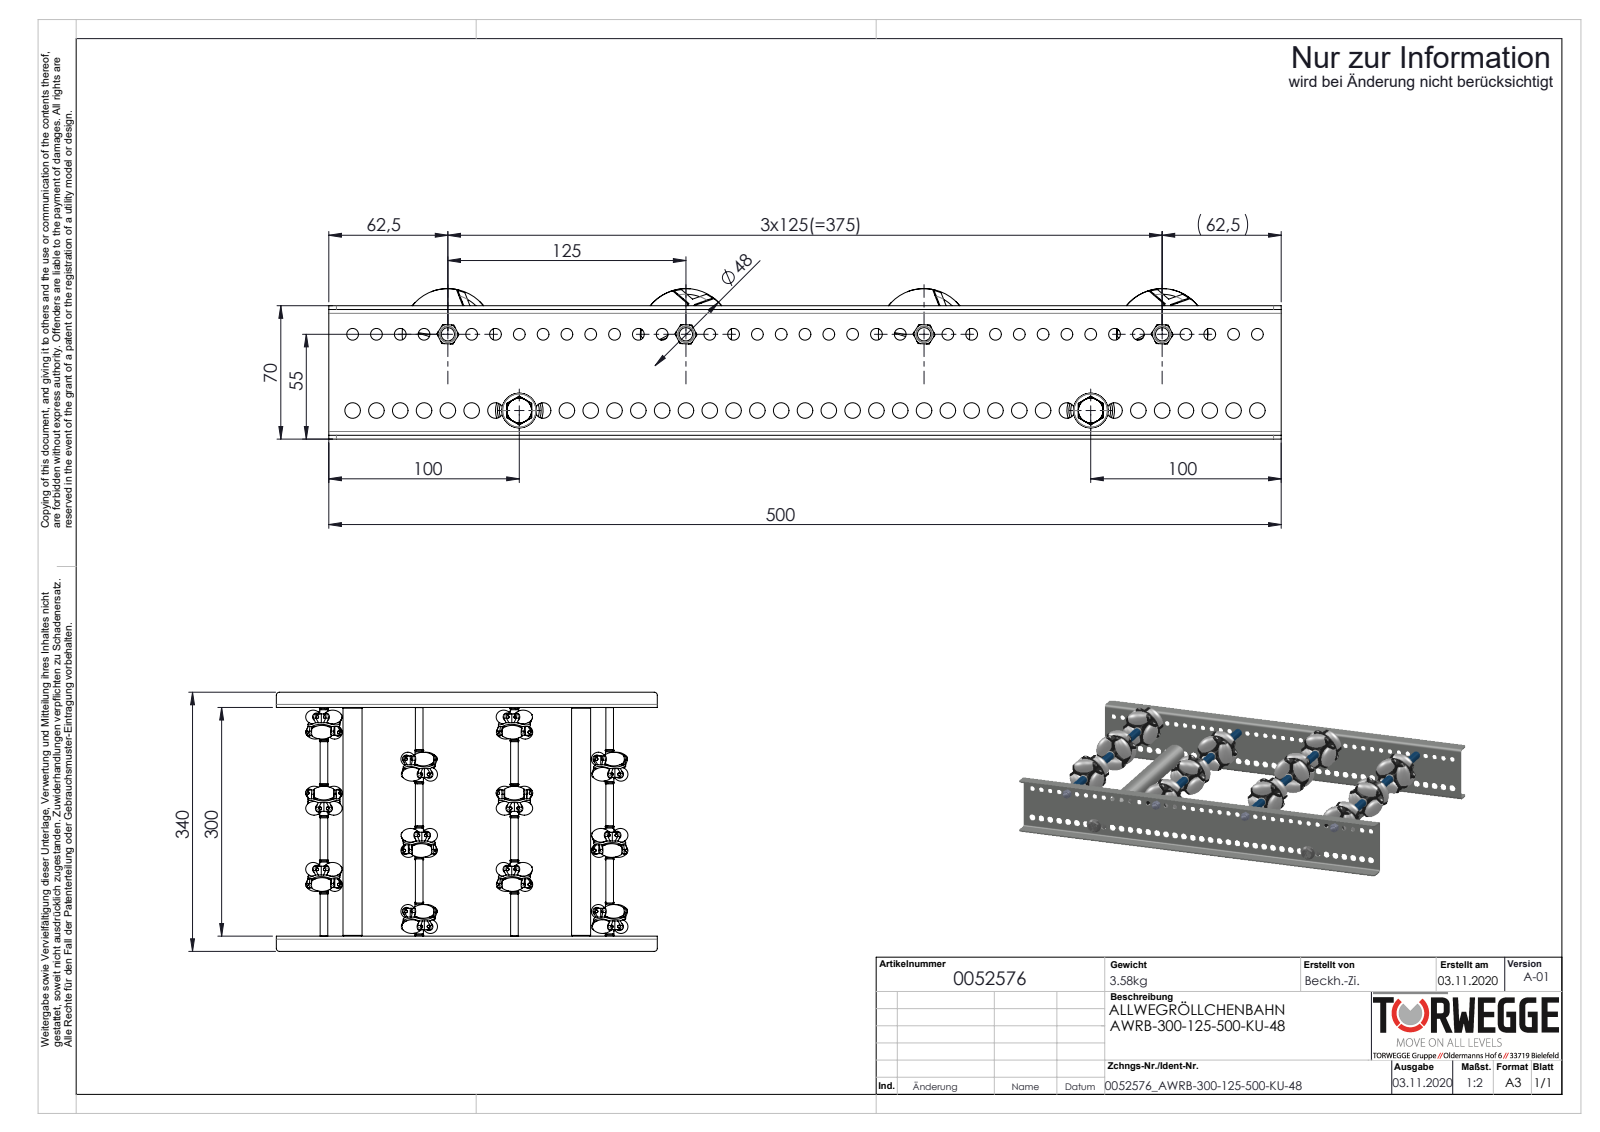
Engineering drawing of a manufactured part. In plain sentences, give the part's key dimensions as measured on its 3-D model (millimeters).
The part is named "0019730_Tragrollenrohr-Ø10x1,75KU_KFG_0019730_L=55; S100994_Sperrzahnschraube_M08x16-8.8-A2K; 0052576; Traversen_KFG_L300 (+8 more)". Its 3-D file was written by "SolidWorks 2020 (AUTOMOTIVE_DESIGN)". It is 216 solids with 4120 faces: 1368 planar, 1656 cylindrical and 1096 other. Overall it measures 500 by 340 by 79 millimeters. Its volume is 886 455 cubic millimeters and its surface area 669 161 square millimeters. Round holes: 72 of diameter 3.7, 72 of diameter 4.2, 39 of diameter 6.2, 39 of diameter 8.2, 4 of diameter 4.92, 4 of diameter 6.5, 4 of diameter 8.4, 2 of diameter 6.8, 2 of diameter 21. Round bosses or shafts: 72 of diameter 4, 60 of diameter 3.7, 6 of diameter 8, 4 of diameter 42, 4 of diameter 11, 4 of diameter 10, 4 of diameter 7, 4 of diameter 6. Partial cylindrical surfaces (rounded edges, fillets, slot ends): 8 of radius 4, 4 of radius 2, 4 of radius 23.55. The main face-to-face distances are 2, 302, 68, 300, 304, 14.75, 70, 66, 3, 11.75. The hole center spacings are 36.05, 36.06, 12.5, 25, 37.5, 50, 62.5, 75.
